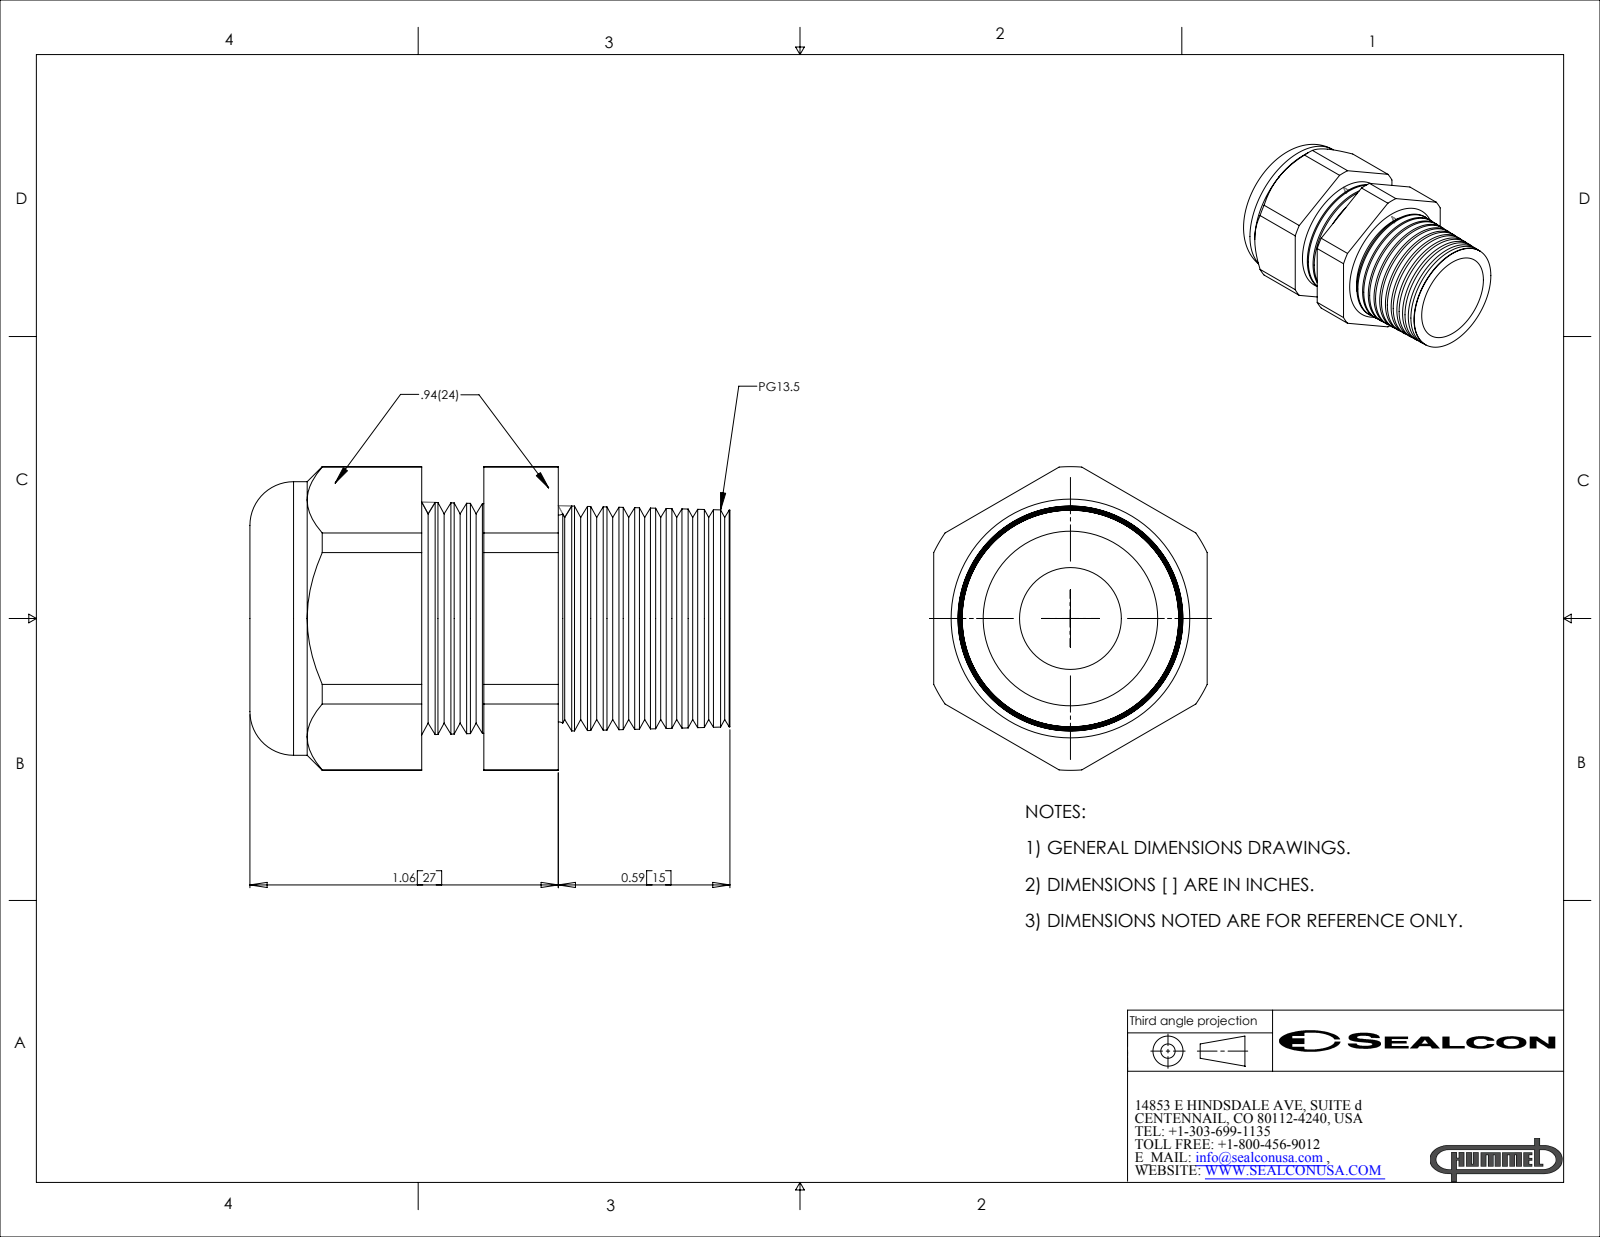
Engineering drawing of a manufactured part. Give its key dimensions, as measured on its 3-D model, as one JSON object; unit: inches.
{"part_name": "CD13CR-BK", "step_written_by": "SolidWorks 2007 (CONFIG_CONTROL_DESIGN)", "units": "inches", "bodies": {"solids": 2, "faces": 148, "planar": 20, "cylindrical": 22, "other": 106}, "overall_size": [1.65, 1.043, 0.94], "volume_in3": 0.708, "surface_area_in2": 10.65, "round_holes": [[0.35, 1], [0.6, 1]], "round_bosses_or_shafts": [[0.94, 1]], "partial_cylinders_radius": [[0.522, 1]], "face_to_face_distances": [0.94, 0.607, 0.394, 0.214, 0.863, 0.47, 0.256, 0.167, 0.561, 0.774]}
